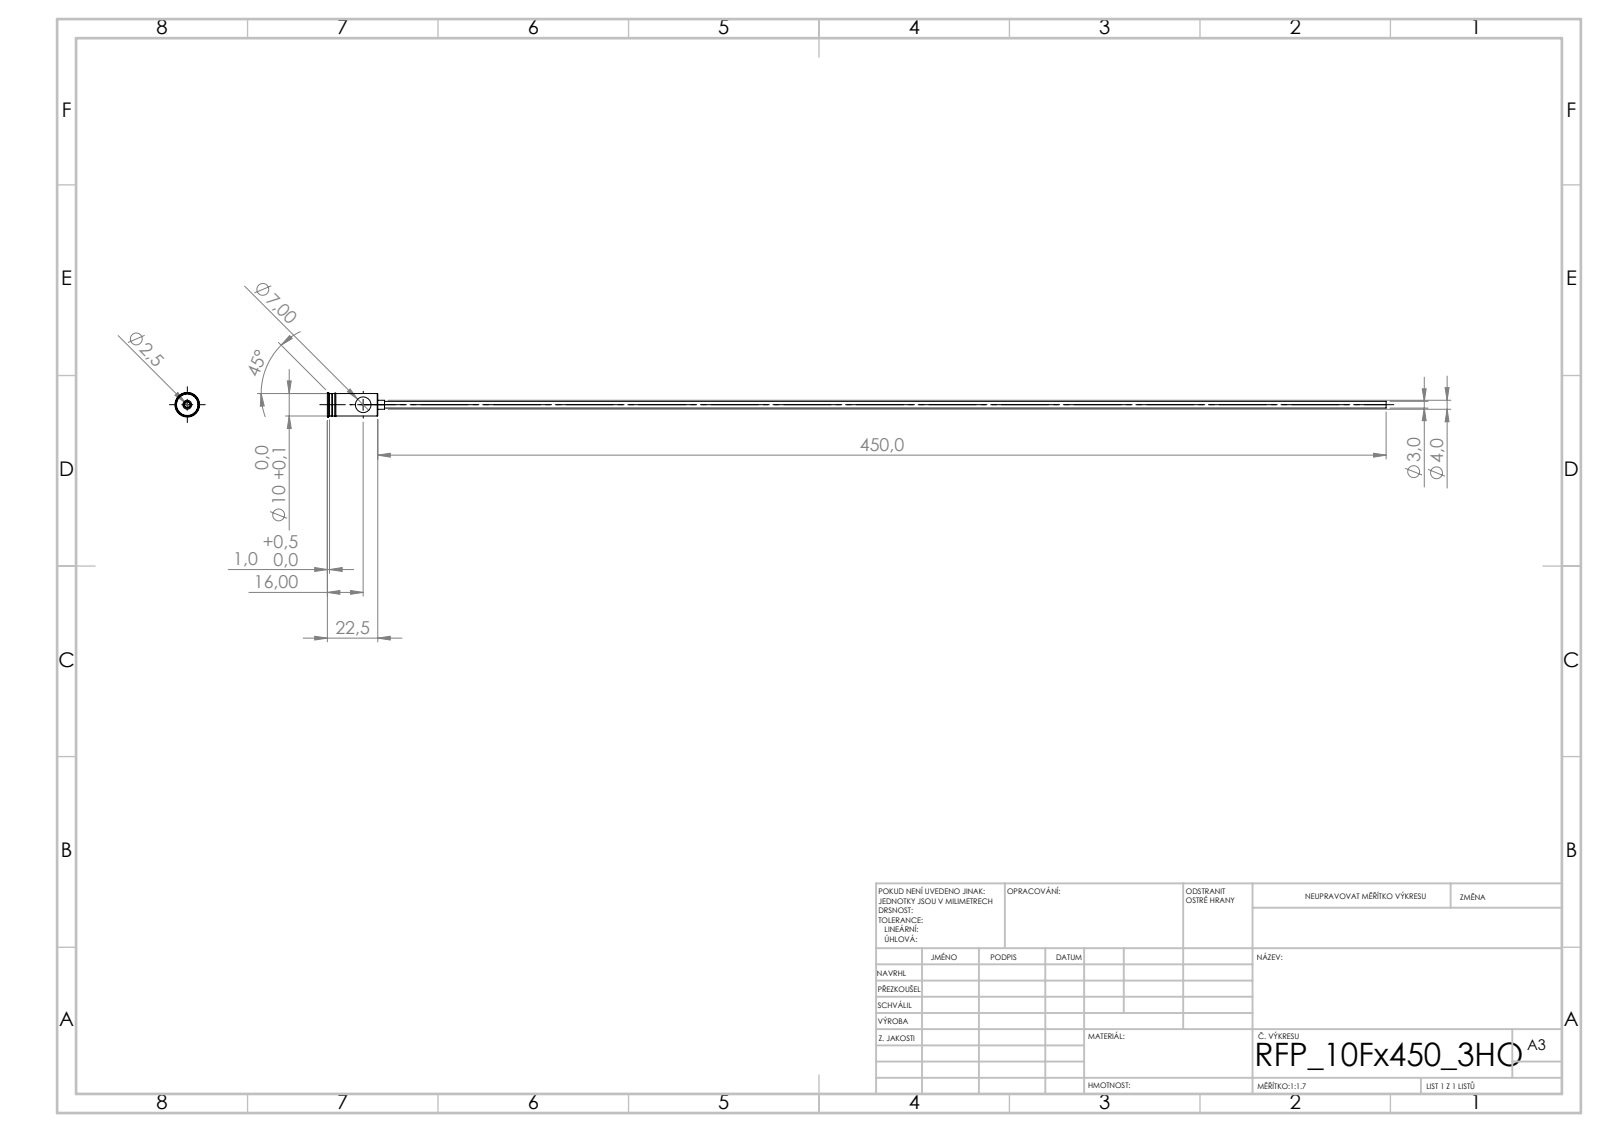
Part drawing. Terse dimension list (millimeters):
written by: SolidWorks 2019 (CONFIG_CONTROL_DESIGN)
unit: mm
bodies: 1 solid, 44 faces (20 planar, 16 cylindrical, 8 other)
size: 472.5 × 11 × 11
volume: 2 344 mm³; area: 8 853 mm²
holes: 1× ⌀2.5, 1× ⌀7
bosses: 1× ⌀11, 1× ⌀10, 1× ⌀4, 1× ⌀3
face distances: 22.5, 20.5, 2, 5.4, 20.2, 2.3, 3, 23.2, 23.5, 25.5
